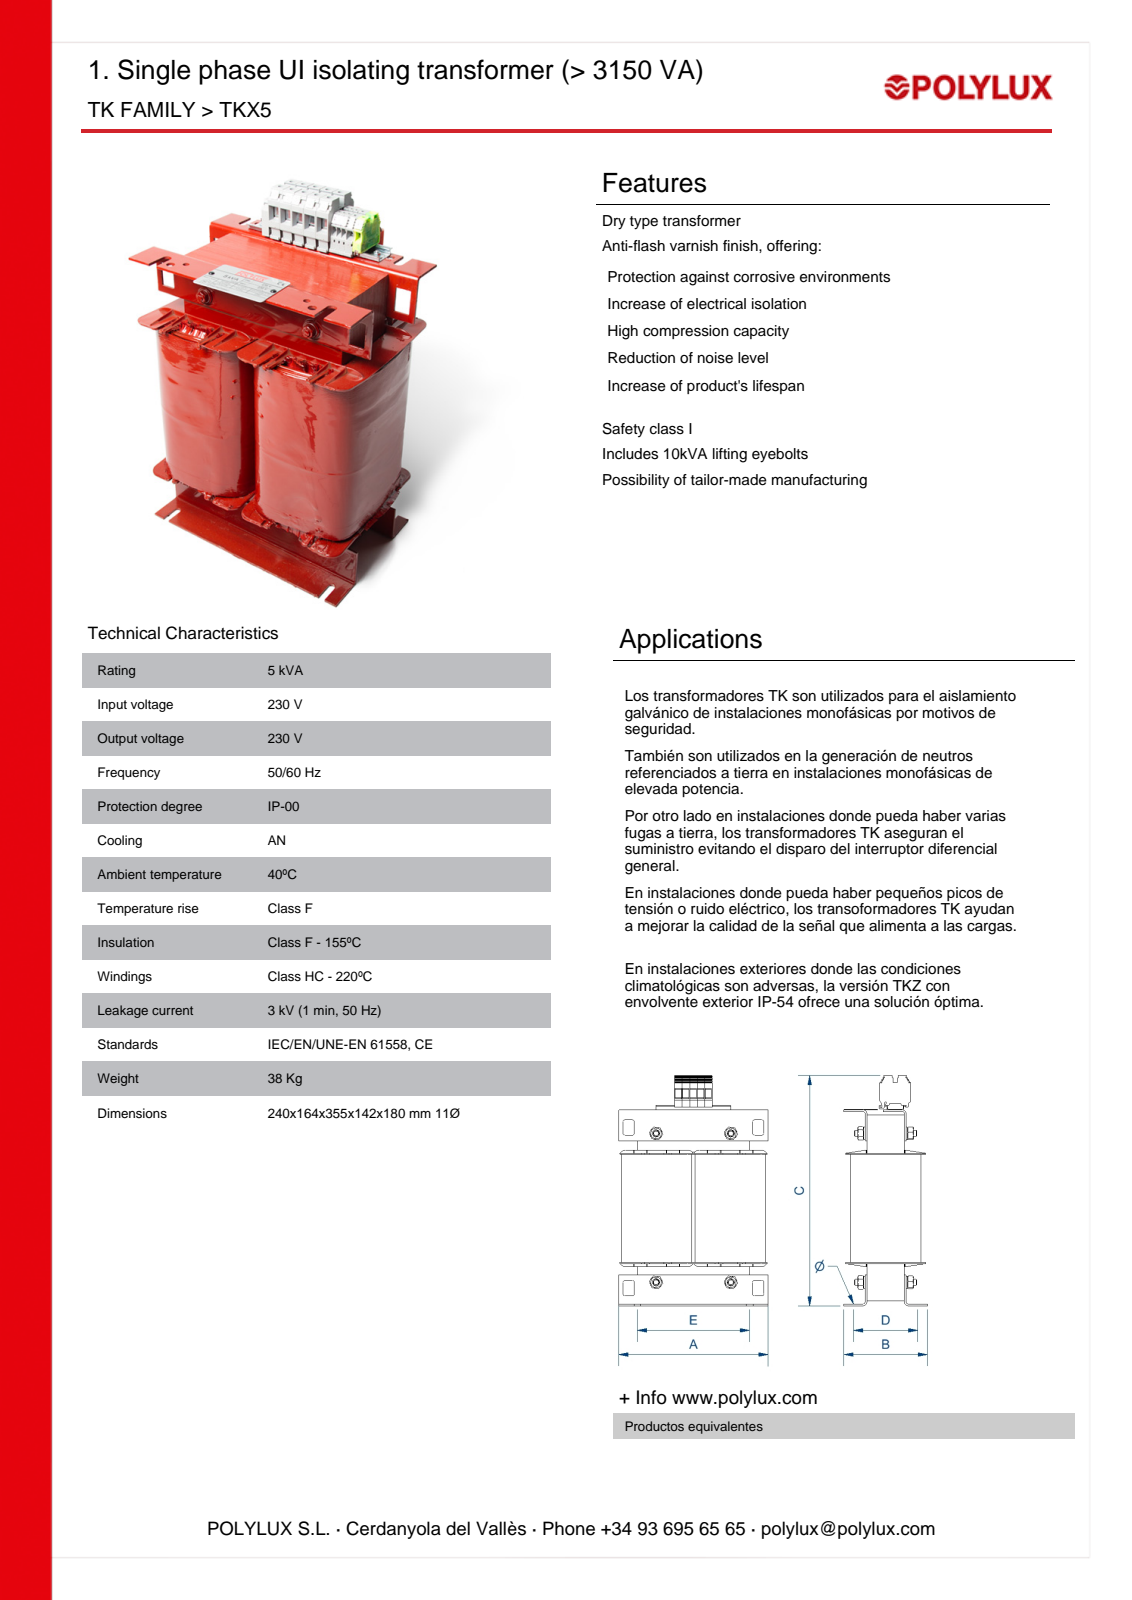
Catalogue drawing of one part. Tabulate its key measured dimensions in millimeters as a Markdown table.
| quantity | value |
| --- | --- |
| part name | TKX5 |
| STEP written by | Autodesk Inventor 2018 (AUTOMOTIVE_DESIGN) |
| units | millimeters |
| bodies | 32 solids, 1739 faces (1258 planar, 457 cylindrical, 24 other) |
| overall size | 371.3 × 240 × 164 |
| volume | 7 937 000 mm³ |
| surface area | 1 123 000 mm² |
| round holes (diameter × count) | 6.4 × 10, 3.5 × 6, 7 × 6, 6.65 × 4, 8.4 × 4, 10 × 4, 12 × 4, 9 × 3, 3 × 1, 5.8 × 1 |
| round bosses / shafts (diameter × count) | 16 × 4, 8 × 4 |
| partial cylindrical surfaces (radius × count) | 0.5 × 51, 10 × 24, 3 × 20, 1 × 12, 2 × 10, 4 × 8, 0.2 × 6, 0.3 × 6 |
| main face-to-face distances | 3, 120, 2, 23.5, 26.5, 93, 1, 63, 25.5, 61 |
| hole center spacings | 12, 23.62, 38, 39.46, 77.23, 116, 56.59, 93 |
